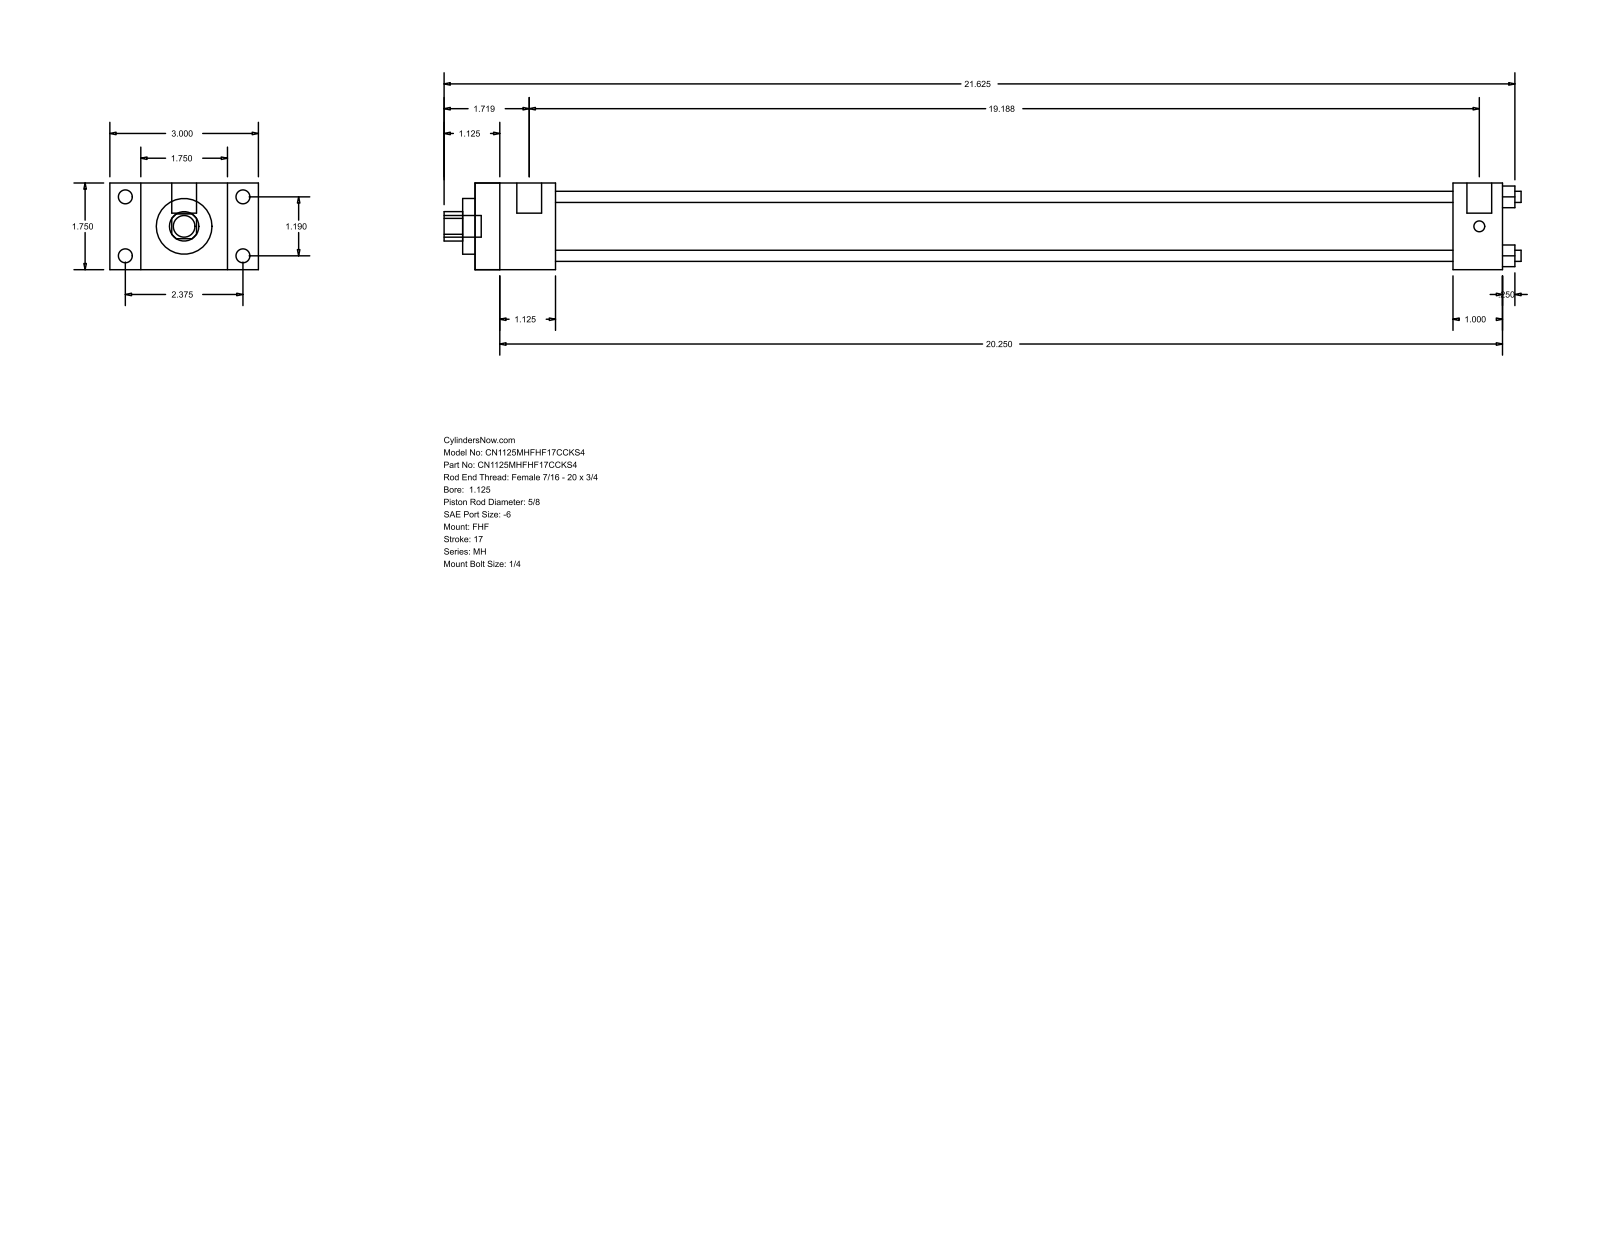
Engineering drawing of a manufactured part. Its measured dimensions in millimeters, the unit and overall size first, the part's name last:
Units: millimetres
Overall size (bounding box): 552.45 × 76.2 × 44.45
Round holes (diameter × count): ⌀5.71 ×4, ⌀15.88 ×1, ⌀28.57 ×1, ⌀34.92 ×1
Round bosses / shafts (diameter × count): ⌀7.14 ×4, ⌀5.56 ×4, ⌀12.7 ×2, ⌀11.11 ×1
Partial cylindrical surfaces — rounded edges, fillets, slot ends (radius × count): R7.54 ×1
Main face-to-face distances: 44.46, 15.87, 60.33, 41.27, 76.2, 527.04, 485.77, 501.64, 460.37, 25.4
Hole centre spacings: 21.37, 30.22, 42.74
Bodies: 0 solids, 88 faces (60 planar, 28 cylindrical, 0 other)
Part name (STEP PRODUCT): MH_FHF__0112_0.625
STEP written by: GSSL Pune (CONFIG_CONTROL_DESIGN)
